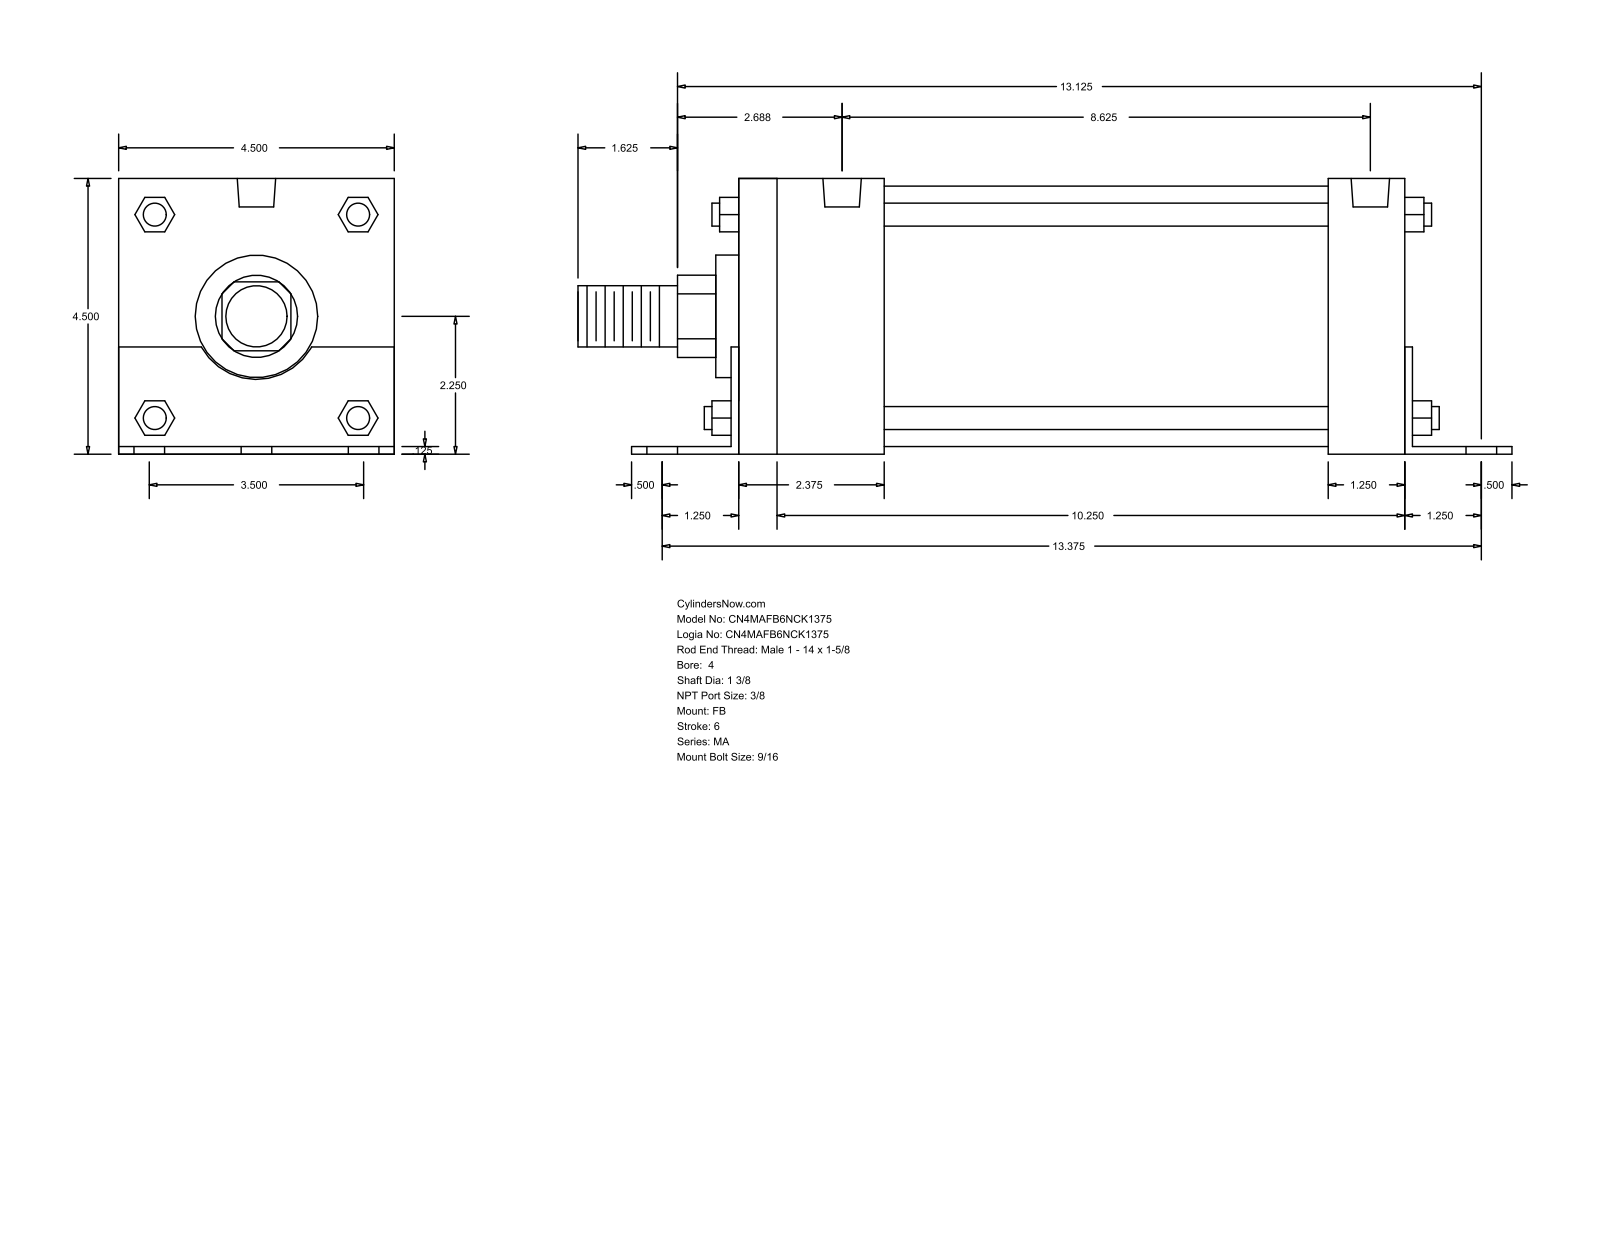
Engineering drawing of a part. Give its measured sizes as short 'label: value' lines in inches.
name: MA_FB__0400_1.375
written by: GSSL Pune (CONFIG_CONTROL_DESIGN)
unit: in
bodies: 0 solids, 140 faces (105 planar, 35 cylindrical, 0 other)
size: 15.25 × 4.502 × 4.5
holes: 6× ⌀0.563, 4× ⌀0.437, 2× ⌀0.627
bosses: 4× ⌀0.375, 1× ⌀4.25, 1× ⌀2, 1× ⌀1.375, 1× ⌀1
rounds: 1× R0.672, 1× R1.03
face distances: 4.5, 0.125, 4.502, 0.123, 4.377, 10.875, 0.125, 11, 11, 11.125
hole spacings: 1.75, 13.489, 13.375, 0.188, 2.52, 2.658, 3.419, 3.5
